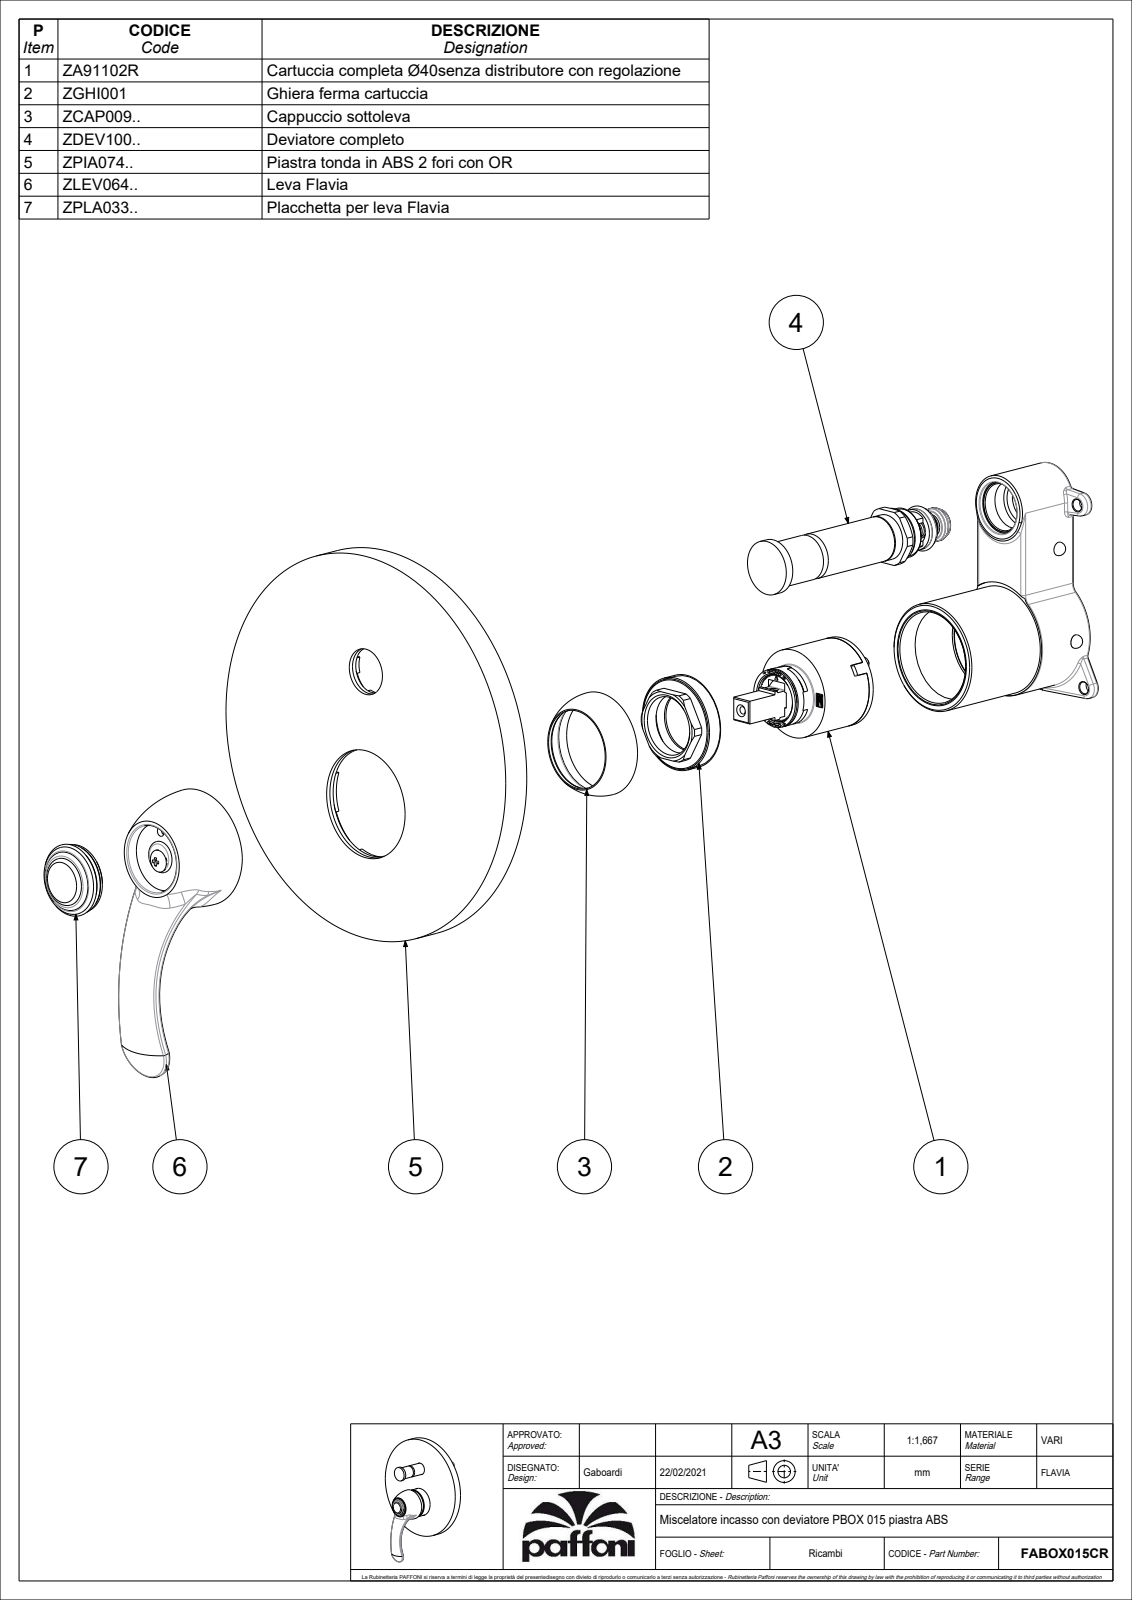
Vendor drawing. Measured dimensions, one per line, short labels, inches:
name: FABOX015CR
written by: CREO PARAMETRIC BY PTC INC, 2020044 (CONFIG_CONTROL_DESIGN)
unit: in
bodies: 8 solids, 1069 faces (630 planar, 257 cylindrical, 182 other)
size: 8.283 × 6.811 × 3.068
volume: 15.62 in³; area: 199.9 in²
holes: 2× ⌀0.157, 1× ⌀0.118, 1× ⌀0.13, 1× ⌀0.197, 1× ⌀0.276, 1× ⌀0.28, 1× ⌀0.63, 1× ⌀0.717, 1× ⌀0.807, 1× ⌀0.827, 1× ⌀0.835, 1× ⌀0.984
bosses: 1× ⌀6.811, 1× ⌀6.575, 1× ⌀2.244, 1× ⌀1.894, 1× ⌀1.555, 1× ⌀1.299, 1× ⌀1.177, 1× ⌀1.142
rounds: 26× R0.02, 24× R0.008, 4× R0.059, 1× R0.256, 1× R0.276, 1× R0.396, 1× R0.423, 1× R0.469
face distances: 0.512, 0.433, 0.079, 0.256, 0.098, 0.394, 1.748, 0.827, 2.26, 1.827
hole spacings: 0.058, 0.064, 0.448, 0.454, 0.512, 0.56, 1.008, 1.014
